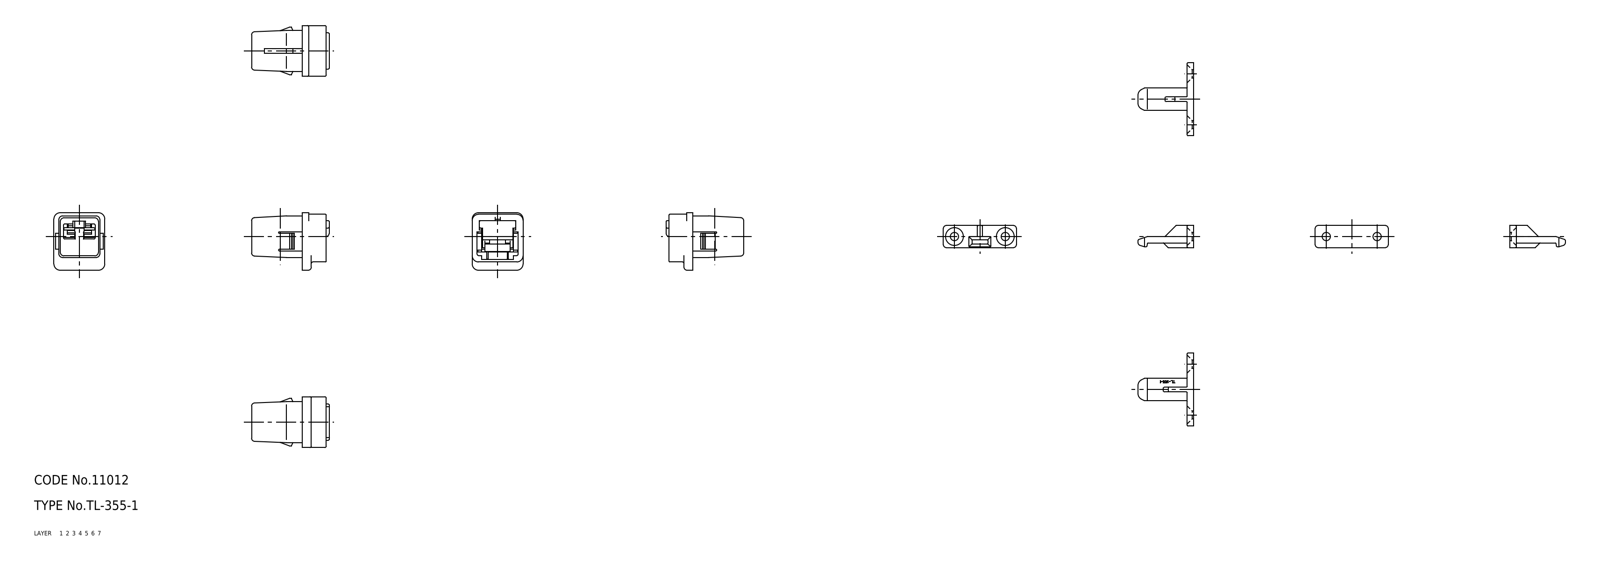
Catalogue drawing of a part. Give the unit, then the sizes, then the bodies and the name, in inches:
Units: inches
Overall size (bounding box): 2.579 × 0.906 × 0.713
Volume: 0.199 in³ · Surface area: 7.342 in²
Bodies: 3 solids, 444 faces (0 planar, 0 cylindrical, 444 other)
Part name (STEP PRODUCT): 67127733; 67127746; 67127759
STEP written by: CADfix (AUTOMOTIVE_DESIGN)
